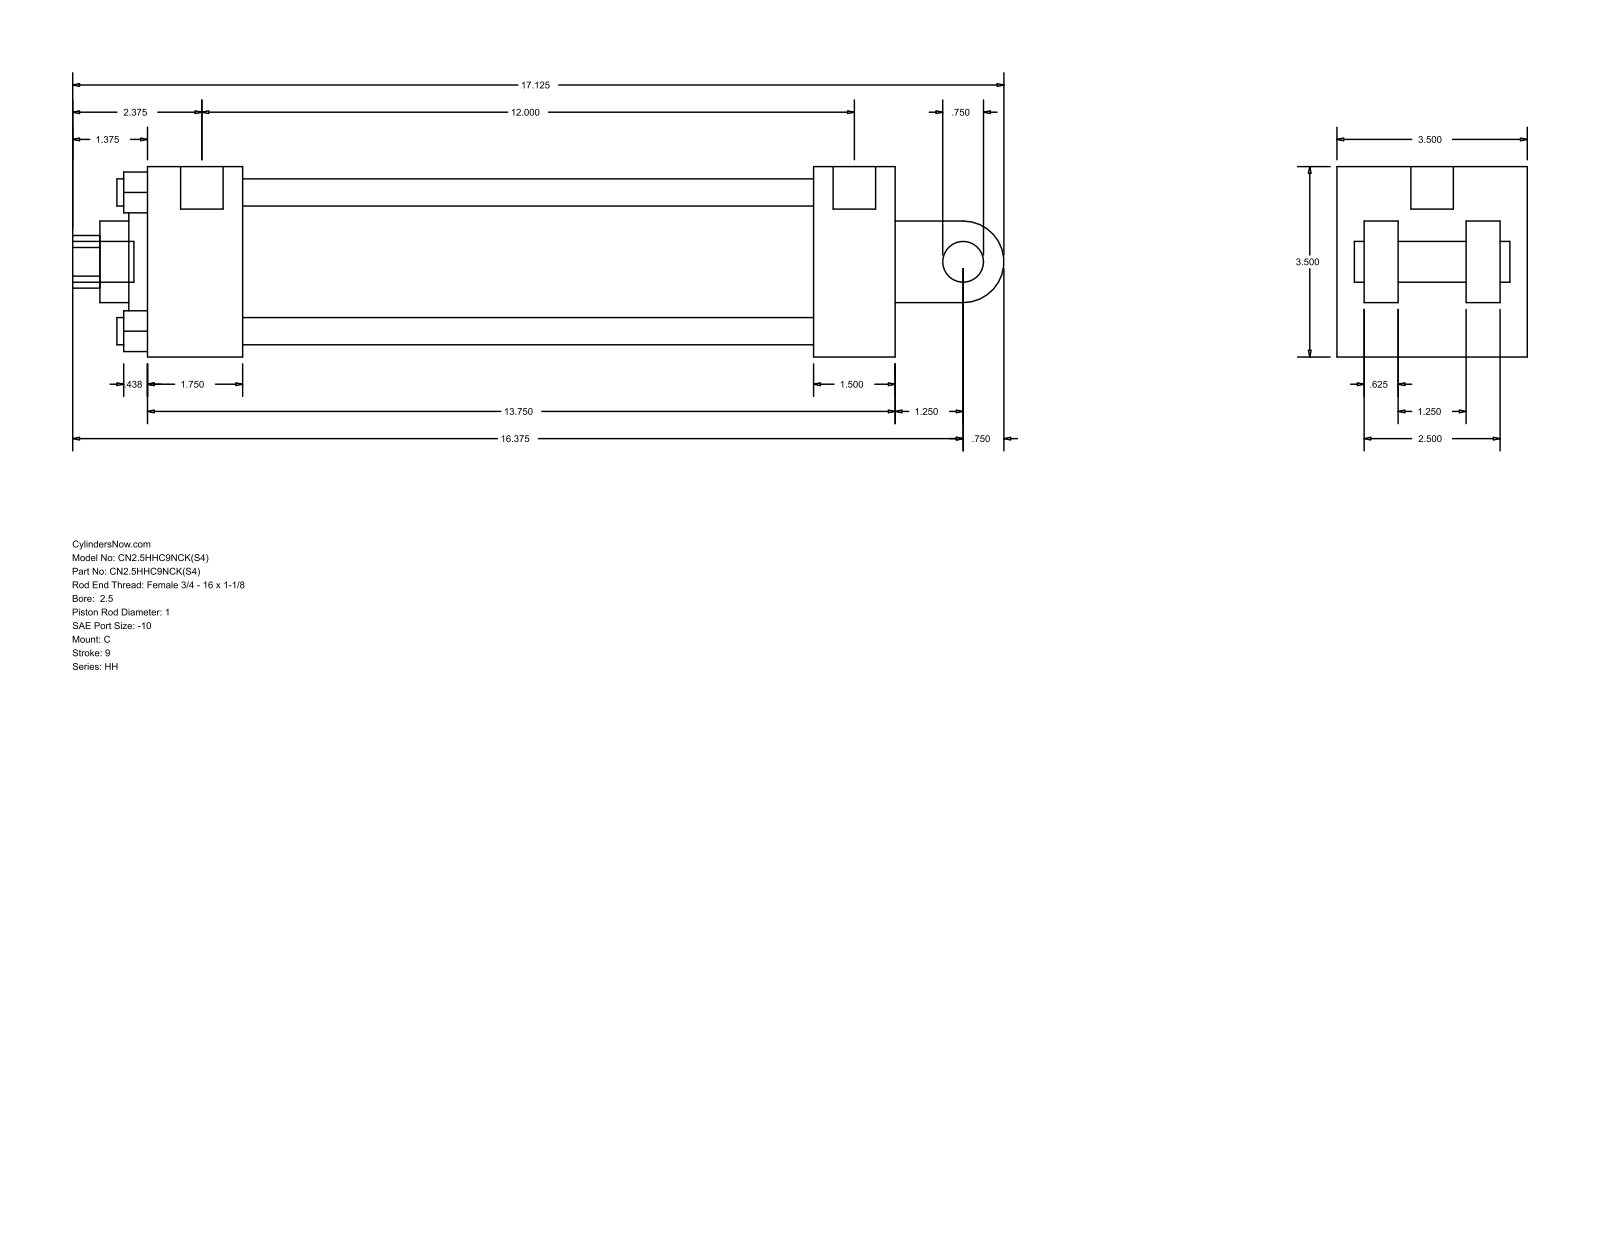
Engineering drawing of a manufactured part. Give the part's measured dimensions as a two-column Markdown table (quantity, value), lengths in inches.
| quantity | value |
| --- | --- |
| part name | HH_C__0250_1 |
| STEP written by | GSSL Pune (CONFIG_CONTROL_DESIGN) |
| units | inches |
| bodies | 0 solids, 101 faces (71 planar, 30 cylindrical, 0 other) |
| overall size | 17.125 × 3.5 × 3.5 |
| round holes (diameter × count) | 0.5 × 4, 0.219 × 2, 0.781 × 1, 1 × 1, 1.5 × 1, 2.375 × 1, 2.875 × 1 |
| round bosses / shafts (diameter × count) | 0.75 × 2, 0.219 × 2, 0.781 × 1 |
| partial cylindrical surfaces (radius × count) | 0.484 × 1, 0.75 × 1 |
| main face-to-face distances | 3.5, 13.75, 2.5, 0.625, 12.25, 1.5, 1.75, 10.5, 12, 0.5 |
| hole center spacings | 1.803, 2.55, 3.606, 0.063 |
